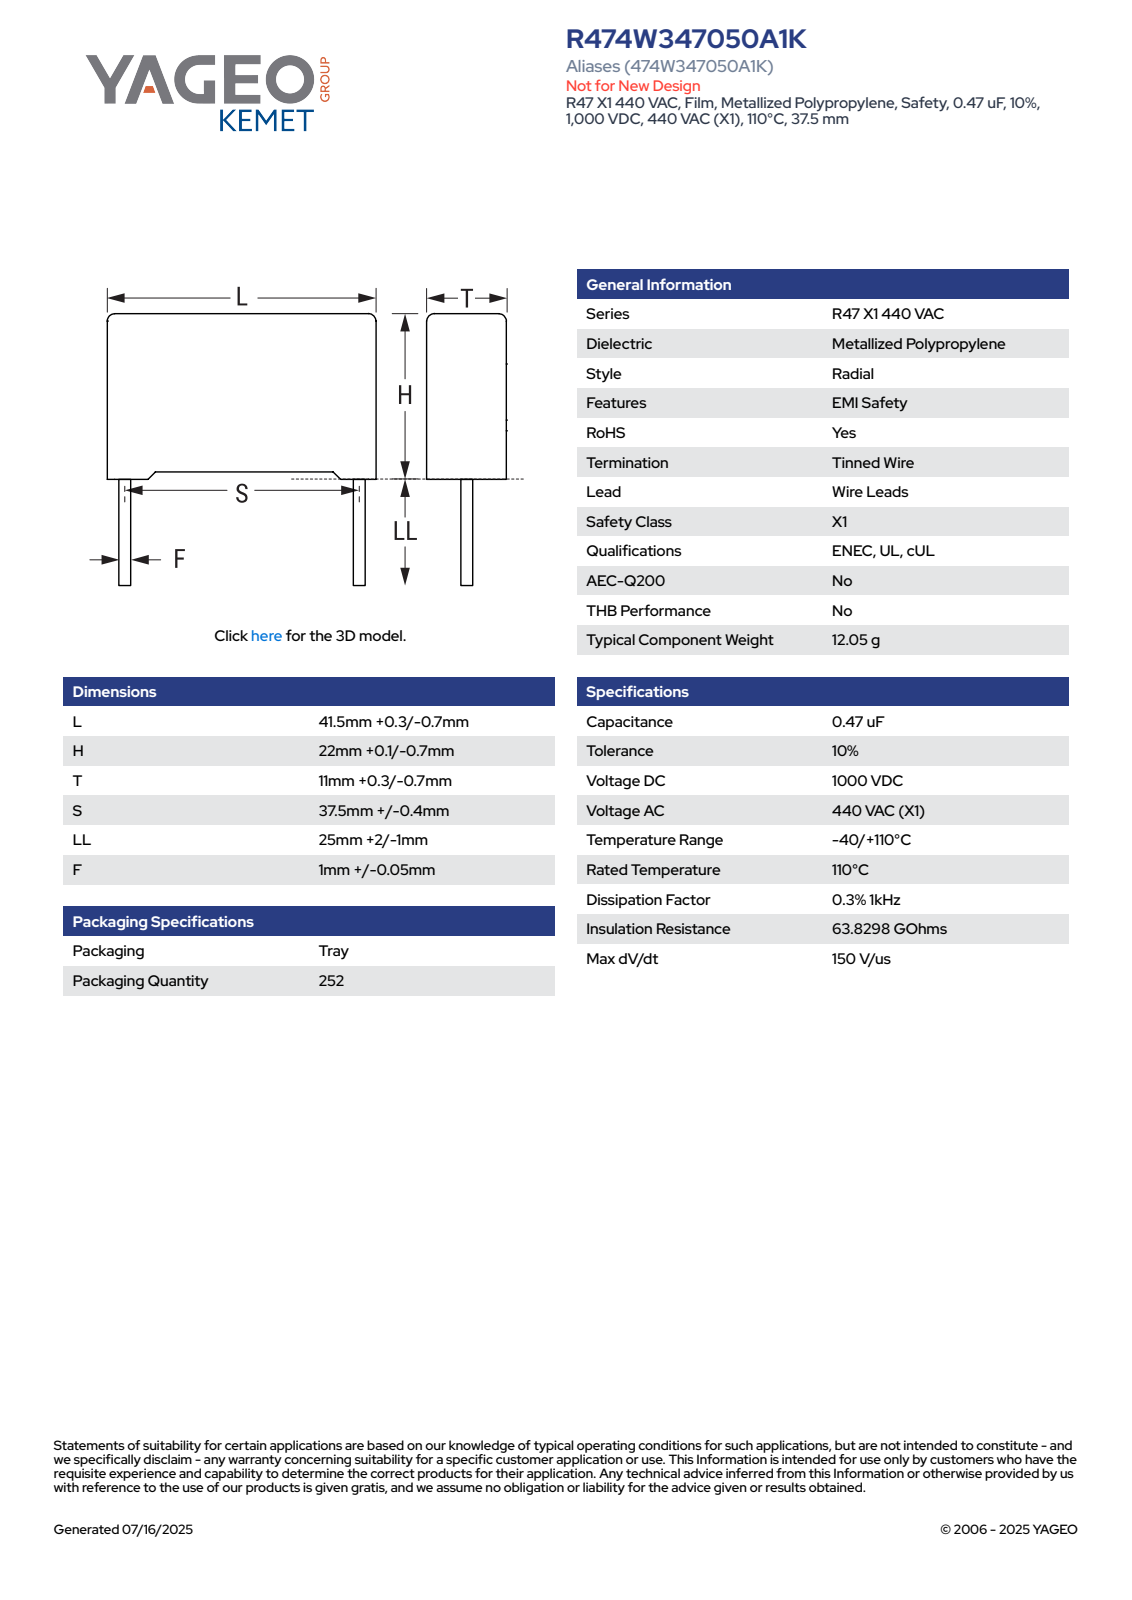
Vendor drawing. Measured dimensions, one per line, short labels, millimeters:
name: CFR_RB2_41.5X22X11_L41.8H22.1T11.3S37.5LL27F1.05
written by: SolidWorks 2021 (AUTOMOTIVE_DESIGN)
unit: mm
bodies: 4 solids, 85 faces (77 planar, 8 cylindrical, 0 other)
size: 49.1 × 41.8 × 11.3
volume: 10 158 mm³; area: 3 554 mm²
bosses: 2× ⌀1.05
rounds: 4× R0.5
face distances: 11.3, 21.34, 41.8, 21.35, 0.75, 0.76, 22.1, 11.31, 1.39, 40.41
